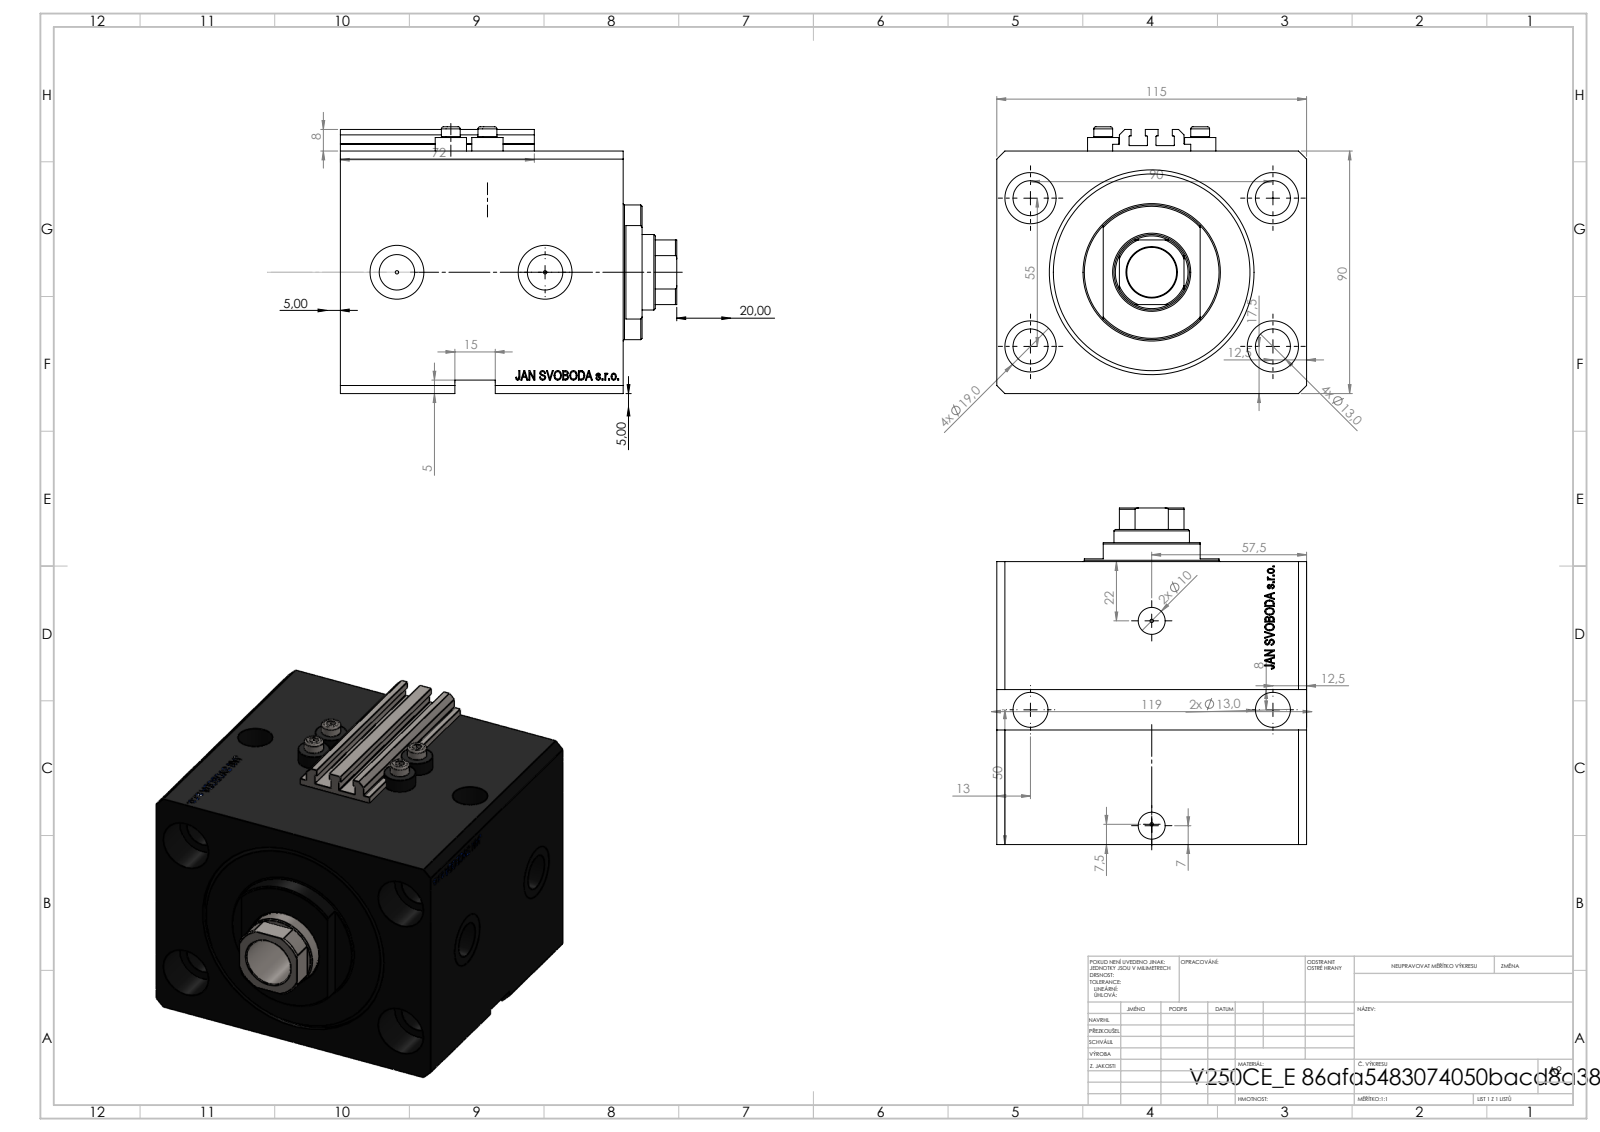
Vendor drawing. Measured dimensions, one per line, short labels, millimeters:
name: V250CE_VC_E; V250CE_C_VCP; V250CE_E_Body; ALLEN BOLT V250CE
written by: SolidWorks 2019 (CONFIG_CONTROL_DESIGN)
unit: mm
bodies: 8 solids, 1123 faces (547 planar, 138 cylindrical, 438 other)
size: 125 × 115 × 99
volume: 950 937 mm³; area: 155 133 mm²
holes: 6× ⌀13, 4× ⌀1.25, 4× ⌀4, 4× ⌀19, 2× ⌀10, 2× ⌀13.16, 2× ⌀20, 1× ⌀18.5, 1× ⌀28, 1× ⌀63, 1× ⌀76
bosses: 4× ⌀11.6, 4× ⌀7, 1× ⌀50
rounds: 10× R0.2, 1× R13.5
face distances: 90, 20, 115, 85, 105, 87.1, 17.9, 67.1, 40, 65
hole spacings: 52.74, 55, 90, 13.6, 27.39, 28.46, 33.62, 36
